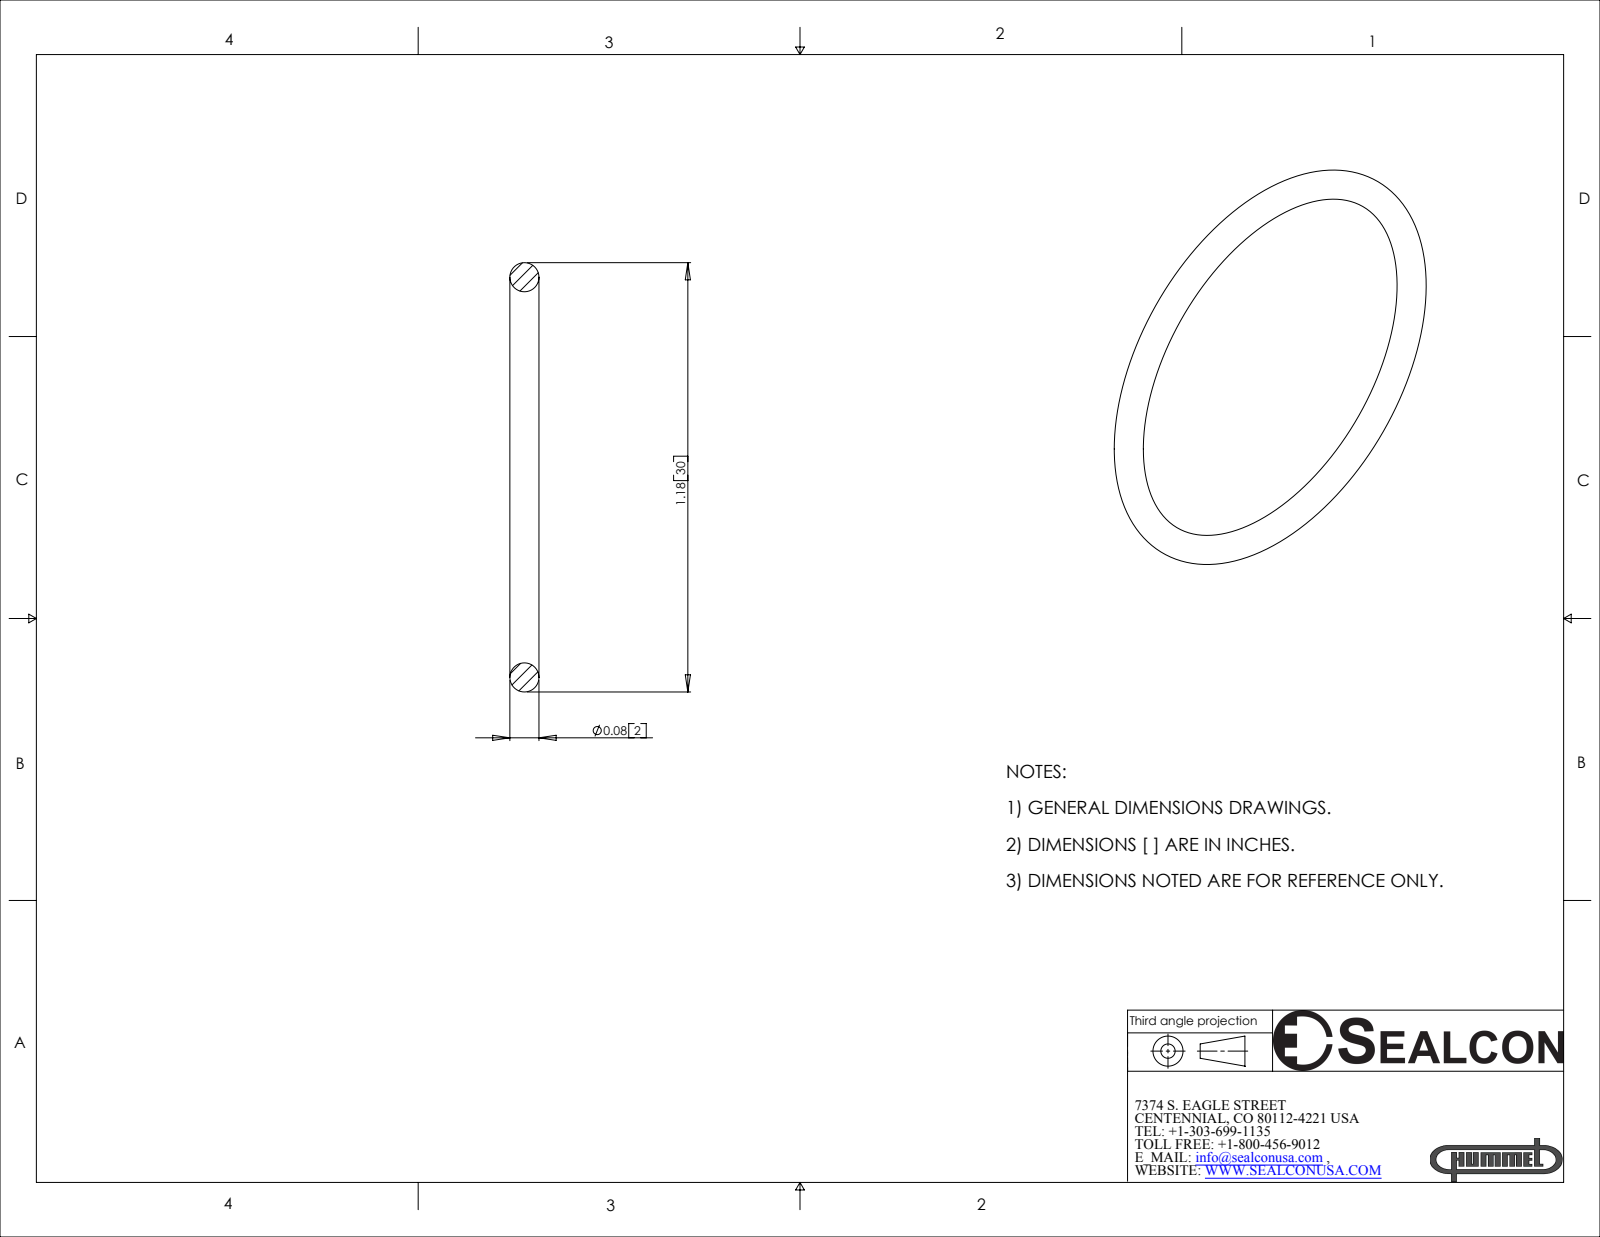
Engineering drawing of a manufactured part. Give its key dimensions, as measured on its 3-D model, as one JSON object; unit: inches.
{"part_name": "OR-21-VT", "step_written_by": "SolidWorks 2007 (CONFIG_CONTROL_DESIGN)", "units": "inches", "bodies": {"solids": 1, "faces": 4, "planar": 0, "cylindrical": 0, "other": 4}, "overall_size": [1.18, 1.18, 0.08], "volume_in3": 0.017, "surface_area_in2": 0.869}
